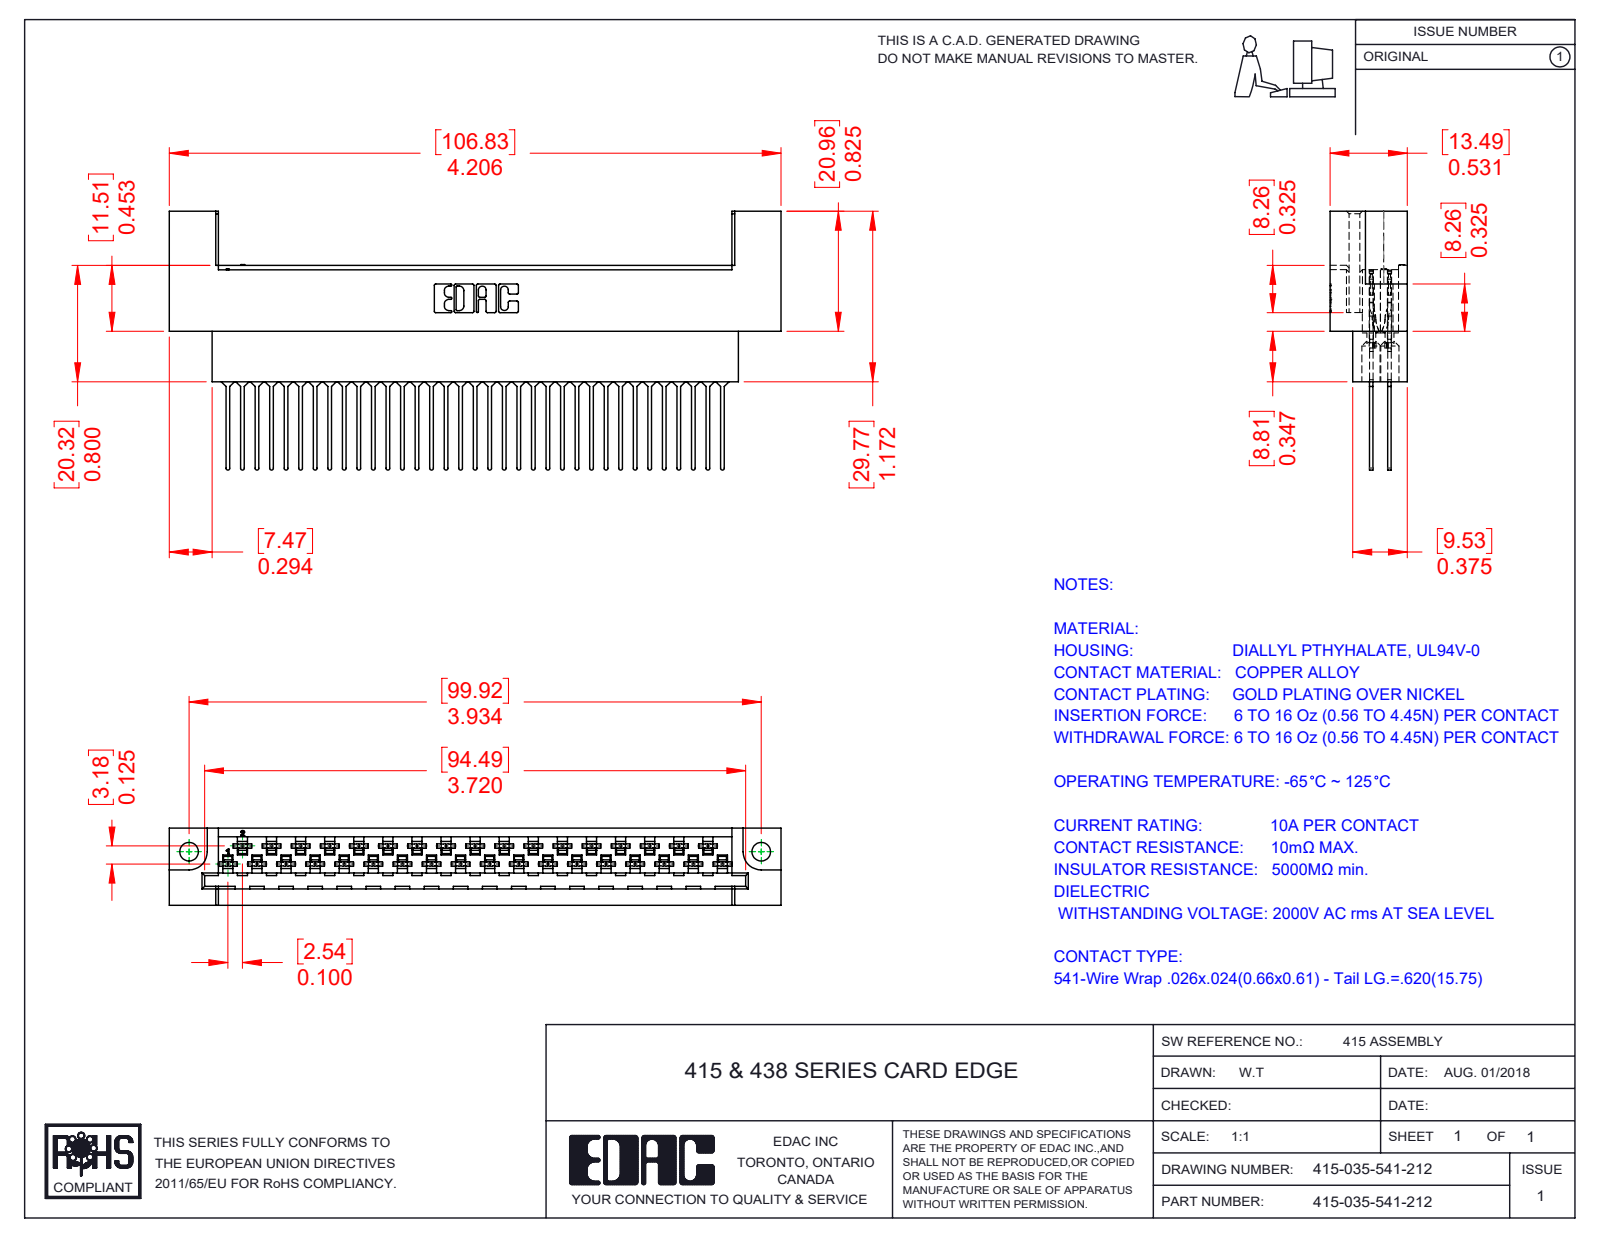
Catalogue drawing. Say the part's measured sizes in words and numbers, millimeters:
The part is named "415-035-541-212; 516-290-001_541; 415-210-001_415-210-035-212". Its 3-D file was written by "SolidWorks 2016 (CONFIG_CONTROL_DESIGN)". It is 36 solids with 3590 faces: 2297 planar, 956 cylindrical and 337 other. Overall it measures 106.83 by 45.17 by 13.49 millimeters. Its volume is 19 084 cubic millimeters and its surface area 23 892 square millimeters. Round holes: 35 of diameter 1.27, 35 of diameter 3.3, 2 of diameter 3.25. Partial cylindrical surfaces (rounded edges, fillets, slot ends): 140 of radius 0.3, 140 of radius 0.56, 70 of radius 0.18, 70 of radius 0.2, 70 of radius 0.41, 70 of radius 2.03, 35 of radius 0.33, 22 of radius 0.25. The main face-to-face distances are 3.18, 0.61, 1.88, 13.49, 1.27, 7.49, 6.61, 6.88, 6, 2.82. The hole center spacings are 5.08, 10.16, 15.24, 20.32, 25.4, 30.48, 35.56, 2.54.
